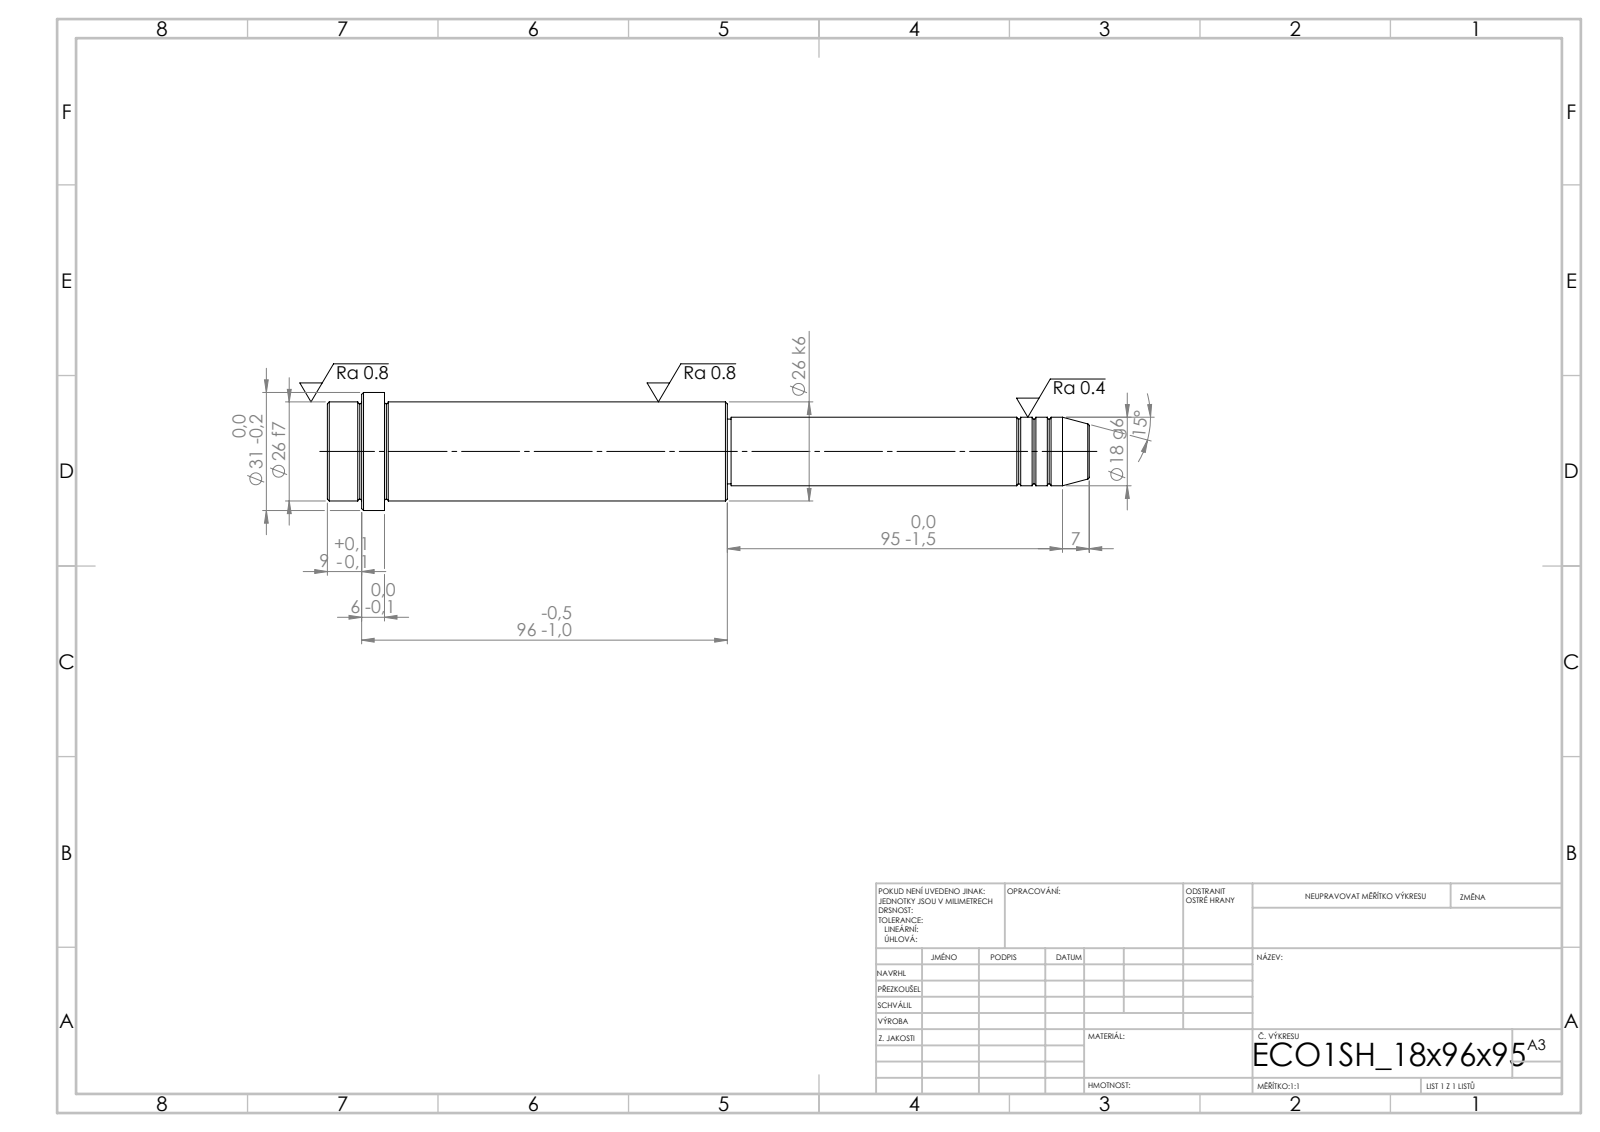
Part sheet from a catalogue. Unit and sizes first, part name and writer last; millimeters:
Units: millimetres
Overall size (bounding box): 200 × 31 × 31
Round bosses / shafts (diameter × count): ⌀31 ×1, ⌀26 ×1, ⌀18 ×1, ⌀17 ×1
Main face-to-face distances: 105, 90, 15, 96, 6, 9, 95, 185, 191, 200
Volume: 80 731 mm³ · Surface area: 15 572 mm²
Bodies: 1 solid, 52 faces (6 planar, 16 cylindrical, 30 other)
STEP written by: SolidWorks 2019 (CONFIG_CONTROL_DESIGN)
